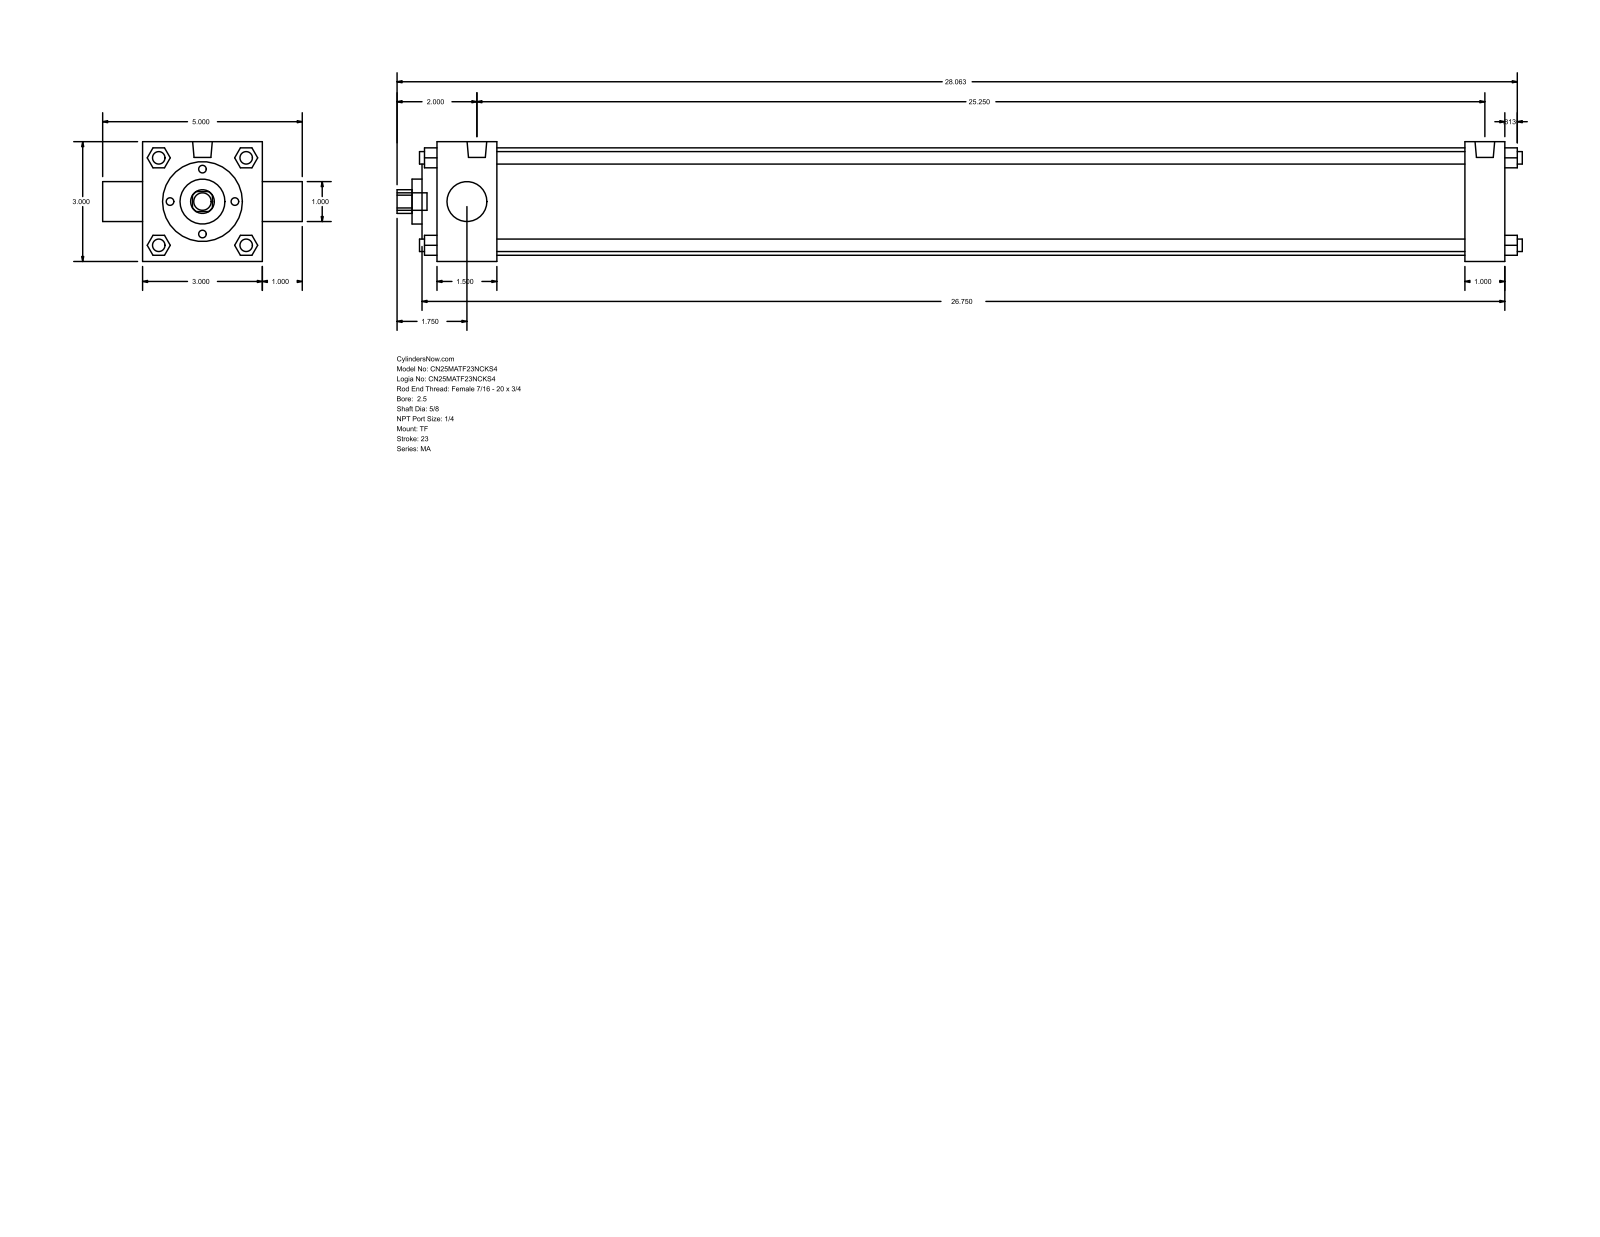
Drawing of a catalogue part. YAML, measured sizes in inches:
part_name: "MA_TF__0250_0.625"
step_written_by: "GSSL Pune (CONFIG_CONTROL_DESIGN)"
units: inches
bodies: {solids: 0, faces: 122, planar: 93, cylindrical: 29, other: 0}
overall_size: [28.187, 5, 3]
round_holes:
  - {diameter: 0.625, count: 1}
  - {diameter: 1, count: 1}
  - {diameter: 1.125, count: 1}
  - {diameter: 2, count: 1}
  - {diameter: 2.69, count: 1}
round_bosses_or_shafts:
  - {diameter: 0.313, count: 7}
  - {diameter: 0.492, count: 2}
  - {diameter: 0.437, count: 1}
partial_cylinders:
  - {radius: 0.297, count: 1}
face_to_face_distances: [3, 26.75, 1, 1.5, 25.75, 24.25, 25.25, 0.5, 0.375, 1.875]
